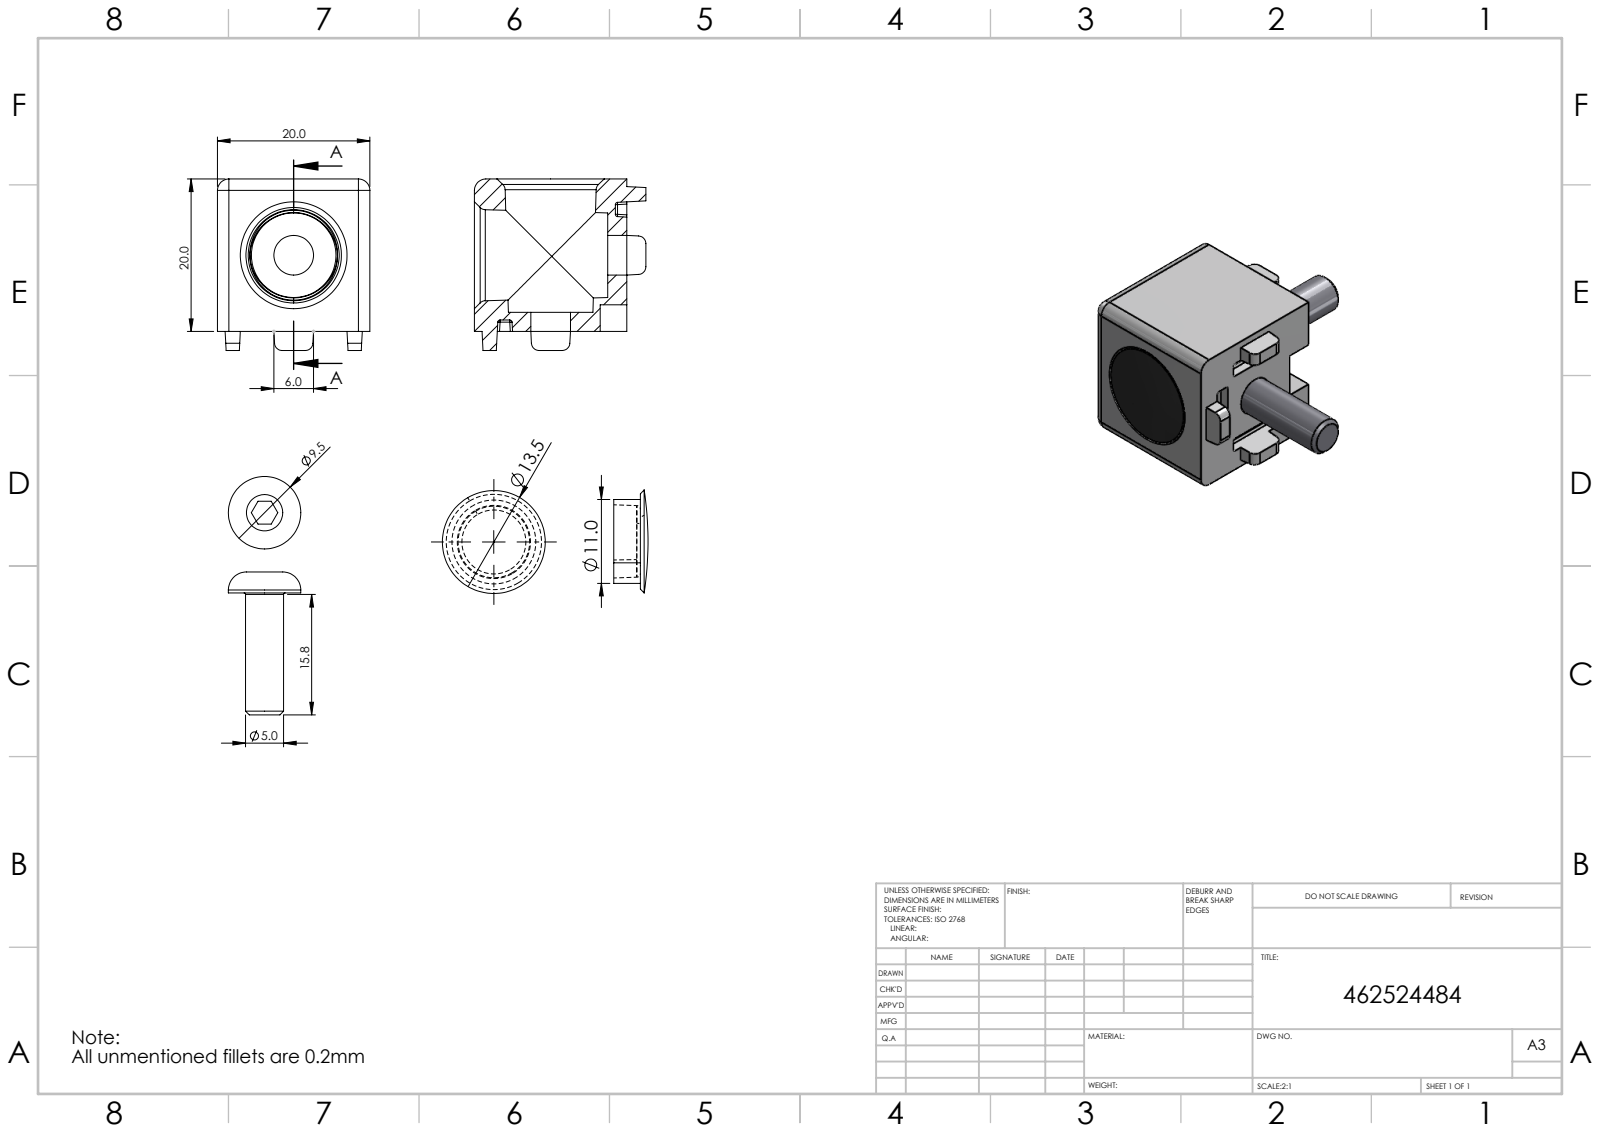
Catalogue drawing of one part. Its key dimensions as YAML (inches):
part_name: "VB-1070_Würfelverbindersatz_2D20-6"
step_written_by: "Autodesk Inventor 2019 (AUTOMOTIVE_DESIGN)"
units: inches
bodies: {solids: 5, faces: 213, planar: 90, cylindrical: 73, other: 50}
overall_size: [1.339, 1.339, 0.787]
volume: 0.389
surface_area: 8.195
round_holes:
  - {diameter: 0.205, count: 2}
round_bosses_or_shafts:
  - {diameter: 0.433, count: 2}
  - {diameter: 0.374, count: 2}
  - {diameter: 0.197, count: 2}
partial_cylinders:
  - {radius: 0.012, count: 44}
  - {radius: 0.039, count: 8}
  - {radius: 0.059, count: 5}
face_to_face_distances: [0.787, 0.098, 0.689, 0.669, 0.768, 0.02, 0.63, 0.039, 0.138, 0.728]
